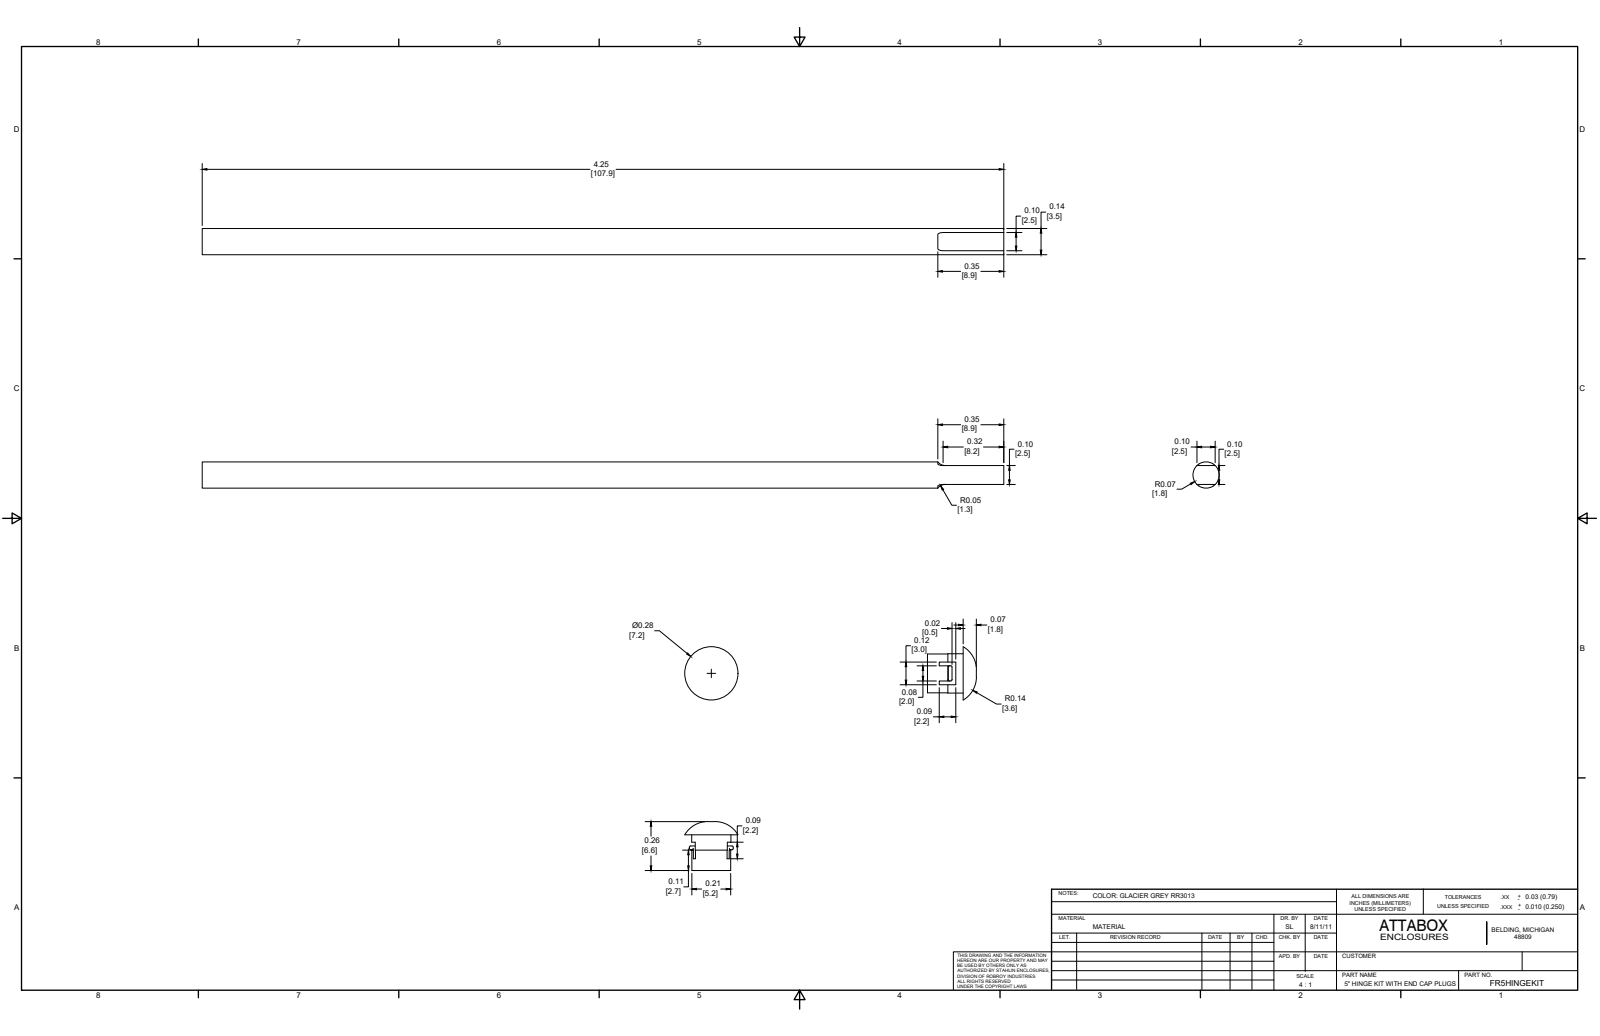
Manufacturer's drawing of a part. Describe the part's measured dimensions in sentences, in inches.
The part is named "FR5HINGEKIT". Its 3-D file was written by "SolidWorks 2019 (AUTOMOTIVE_DESIGN)". It is 6 solids with 252 faces: 136 planar, 86 cylindrical and 30 other. Overall it measures 4.383 by 2.361 by 1.389 inches. Its volume is 0.143 cubic inches and its surface area 5.097 square inches. Round holes: 4 of diameter 0.131. Round bosses or shafts: 4 of diameter 0.208, 4 of diameter 0.206, 2 of diameter 0.135. Partial cylindrical surfaces (rounded edges, fillets, slot ends): 32 of radius 0.006, 12 of radius 0.008, 4 of radius 0.401. The main face-to-face distances are 0.093, 0.096, 0.189, 0.598, 0.595, 0.502, 0.02, 0.1, 0.15, 0.039. The hole center spacings are 0.407, 0.522, 0.831, 0.859, 1.093, 1.499.
